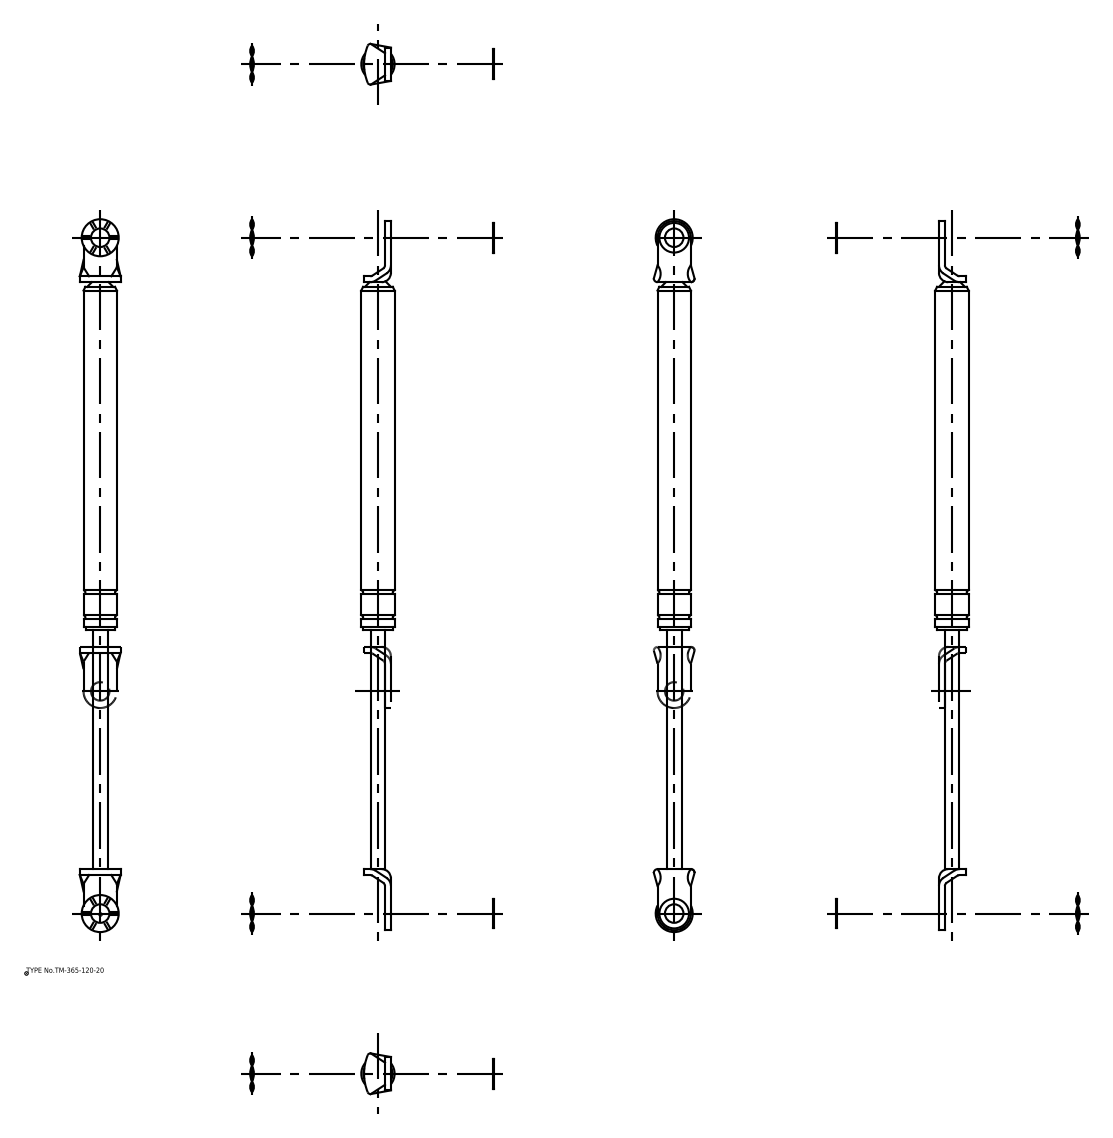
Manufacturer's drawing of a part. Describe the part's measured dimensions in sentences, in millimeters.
The part is named "ウェーブワッシャー; ワッシャー; 本体; 本体_div". Its 3-D file was written by "spGate 16.7.1 (AUTOMOTIVE_DESIGN)". It is 6 solids with 94 faces: 42 planar, 44 cylindrical and 8 other. Overall it measures 385 by 22 by 18.5 millimeters. Its volume is 59 302 cubic millimeters and its surface area 19 886 square millimeters. Round holes: 2 of diameter 10. Round bosses or shafts: 3 of diameter 16, 2 of diameter 20, 1 of diameter 18.5, 1 of diameter 18, 1 of diameter 8. Partial cylindrical surfaces (rounded edges, fillets, slot ends): 2 of radius 4.4, 2 of radius 5, 2 of radius 9, 1 of radius 26.32. The main face-to-face distances are 3.2, 2, 5.2, 320.2, 3.7, 5.7, 0.5, 191.2, 132.2, 323.4. The hole center spacings are 365.
